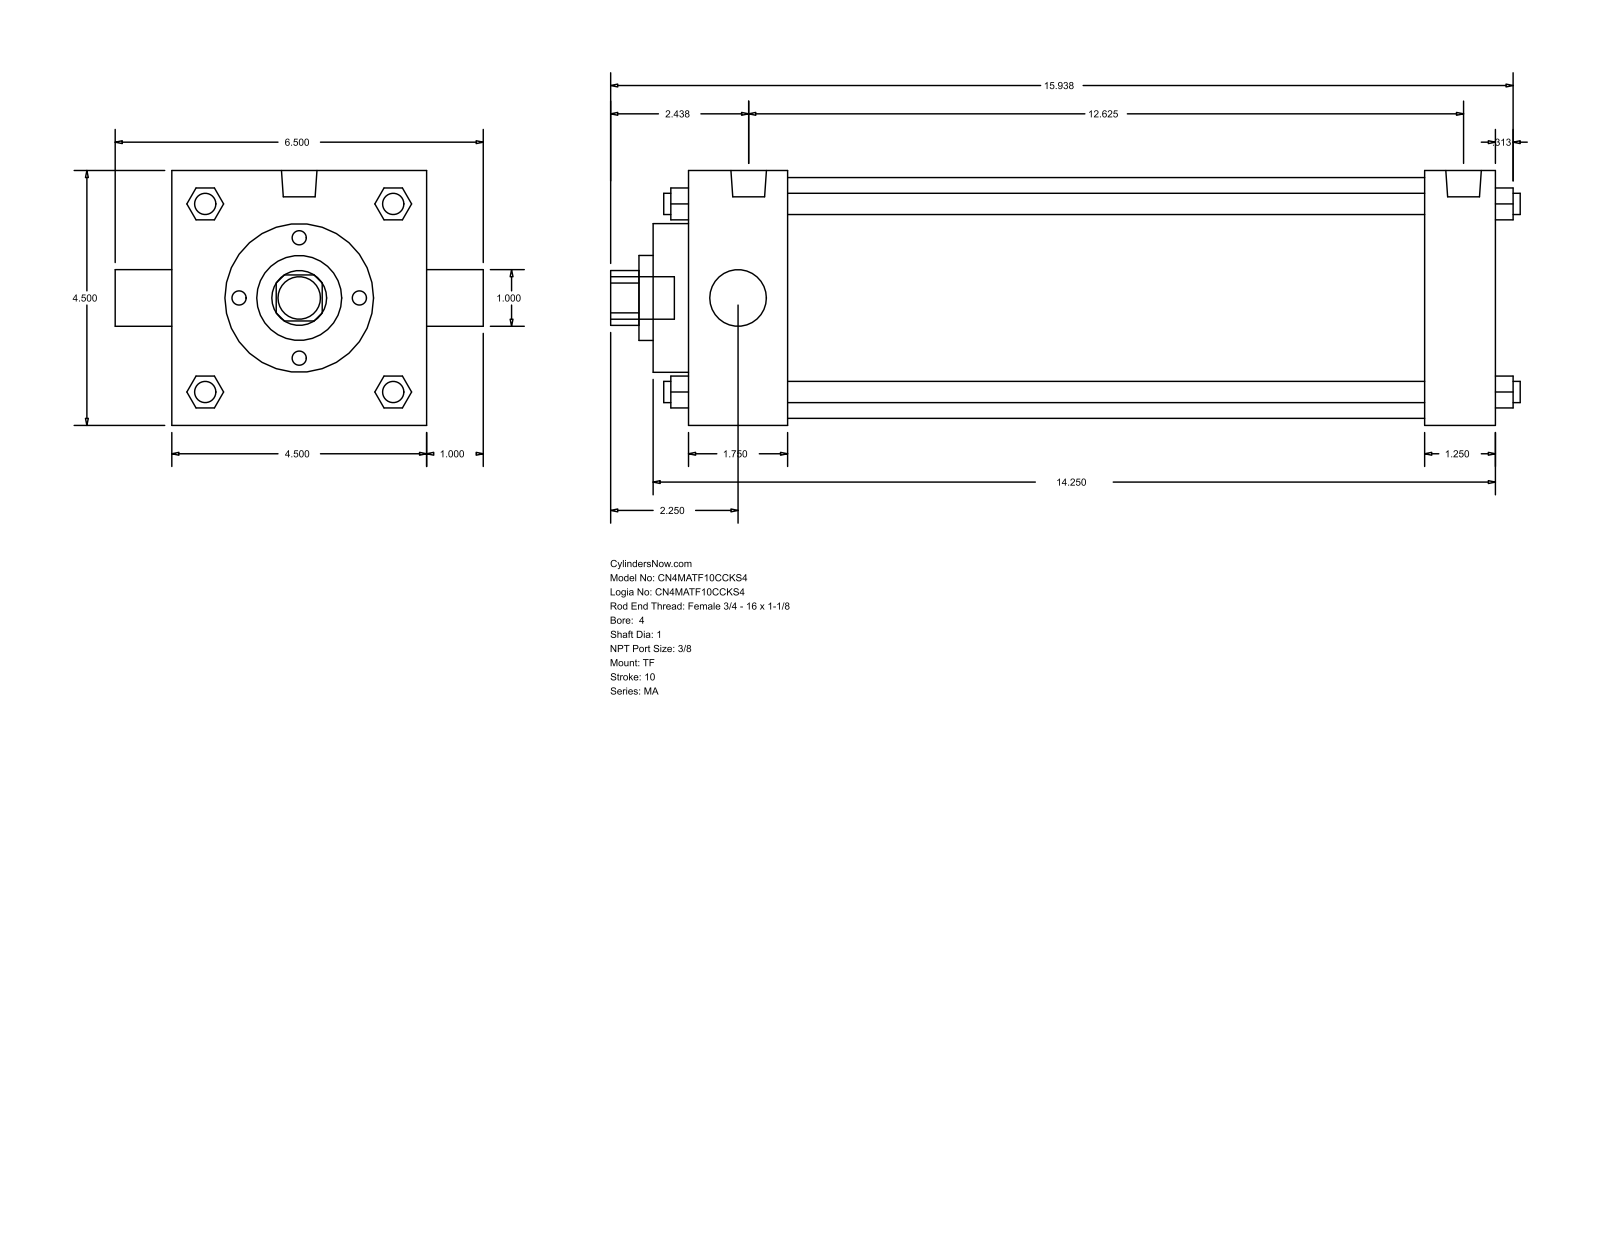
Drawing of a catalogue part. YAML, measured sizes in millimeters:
part_name: "MA_TF__0400_1"
step_written_by: "GSSL Pune (CONFIG_CONTROL_DESIGN)"
units: millimeters
bodies: {solids: 0, faces: 122, planar: 93, cylindrical: 29, other: 0}
overall_size: [407.99, 165.1, 114.3]
round_holes:
  - {diameter: 25.4, count: 2}
  - {diameter: 38.1, count: 1}
  - {diameter: 66.67, count: 1}
  - {diameter: 107.95, count: 1}
round_bosses_or_shafts:
  - {diameter: 9.53, count: 4}
  - {diameter: 11.11, count: 3}
  - {diameter: 15.93, count: 2}
  - {diameter: 19.05, count: 1}
partial_cylinders:
  - {radius: 12.29, count: 1}
face_to_face_distances: [114.3, 361.96, 330.2, 31.76, 44.46, 285.74, 317.5, 15.87, 60.33, 346.07]
